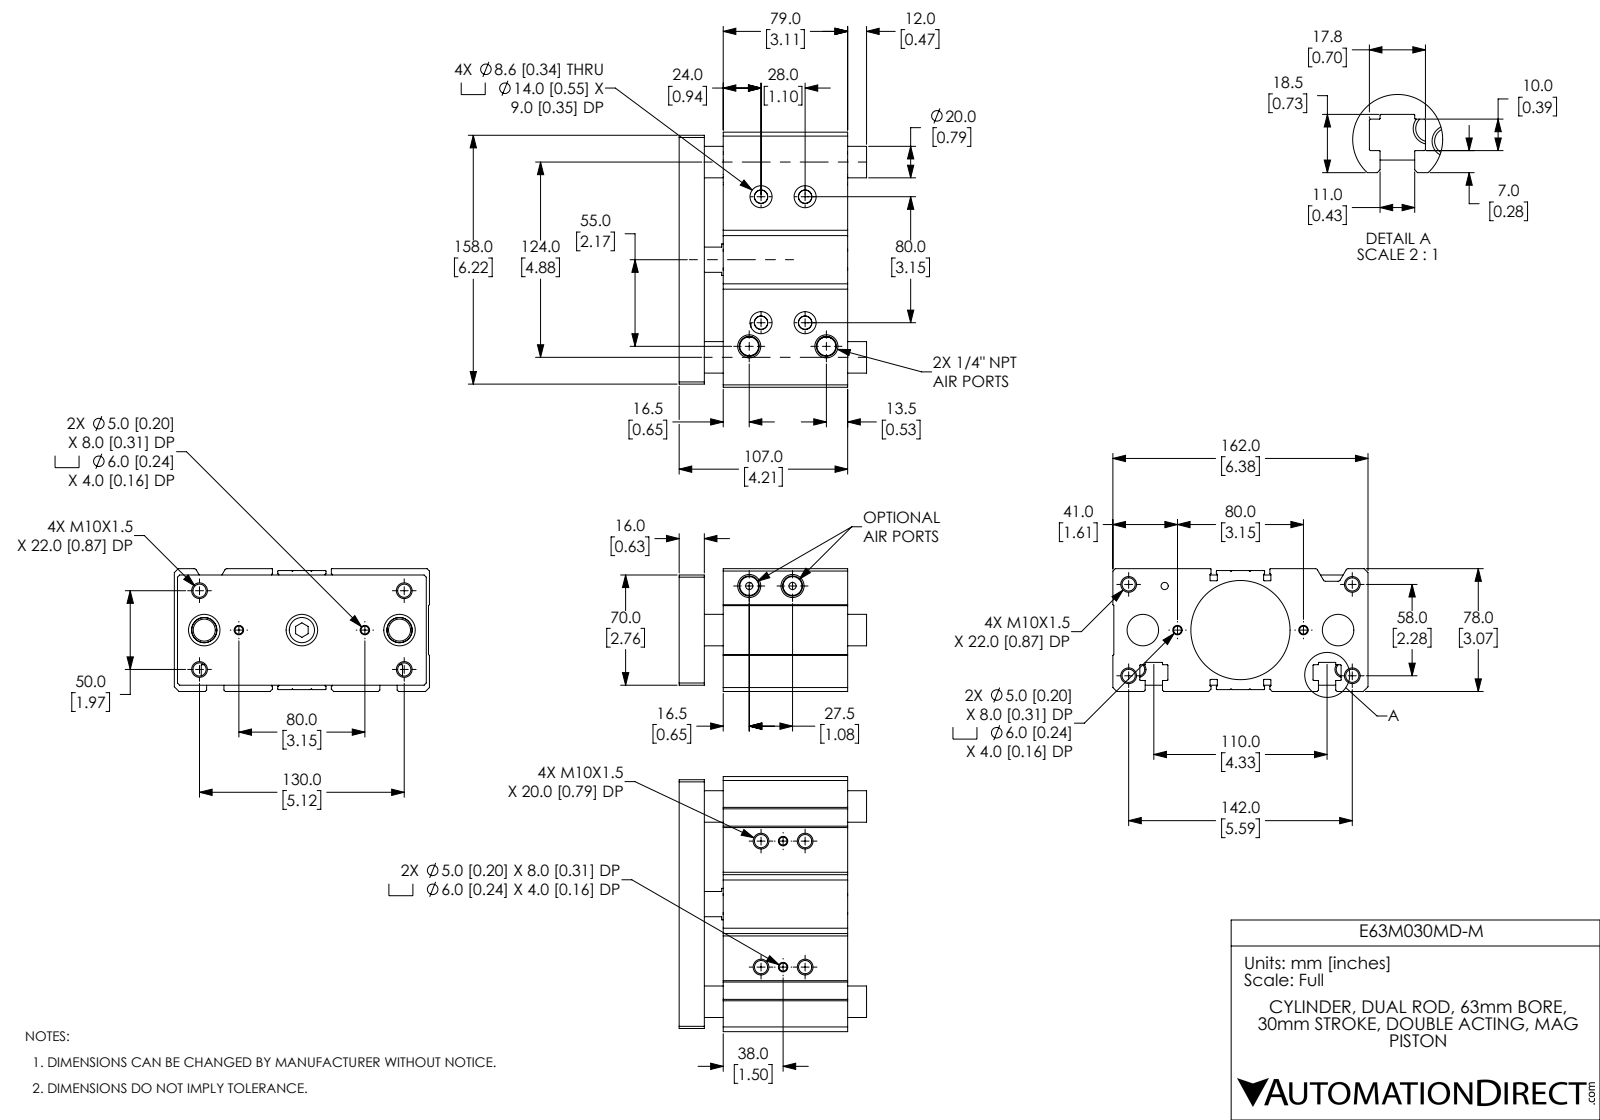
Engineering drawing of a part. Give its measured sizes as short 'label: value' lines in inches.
name: E63M030MD-M_BODY; E63M030MD-M; E63M030MD-M_ENDPLATE
written by: SolidWorks 2019 (CONFIG_CONTROL_DESIGN)
unit: in
bodies: 5 solids, 421 faces (139 planar, 190 cylindrical, 92 other)
size: 6.378 × 4.685 × 3.071
volume: 60.54 in³; area: 282.9 in²
holes: 12× ⌀0.33, 4× ⌀0.197, 4× ⌀0.236, 4× ⌀0.339, 4× ⌀0.551, 3× ⌀0.18, 3× ⌀0.394, 3× ⌀0.787, 2× ⌀0.63, 1× ⌀0.787, 1× ⌀2.48, 1× ⌀2.48
bosses: 1× ⌀0.63
rounds: 32× R0.008, 28× R0.016, 4× R0.059, 2× R0.012
face distances: 0.472, 1.102, 0.63, 3.583, 4.213, 3.11, 3.071, 0.157, 3.947, 3.317
hole spacings: 0.284, 0.551, 0.991, 1.195, 1.392, 1.671, 2.139, 2.742
